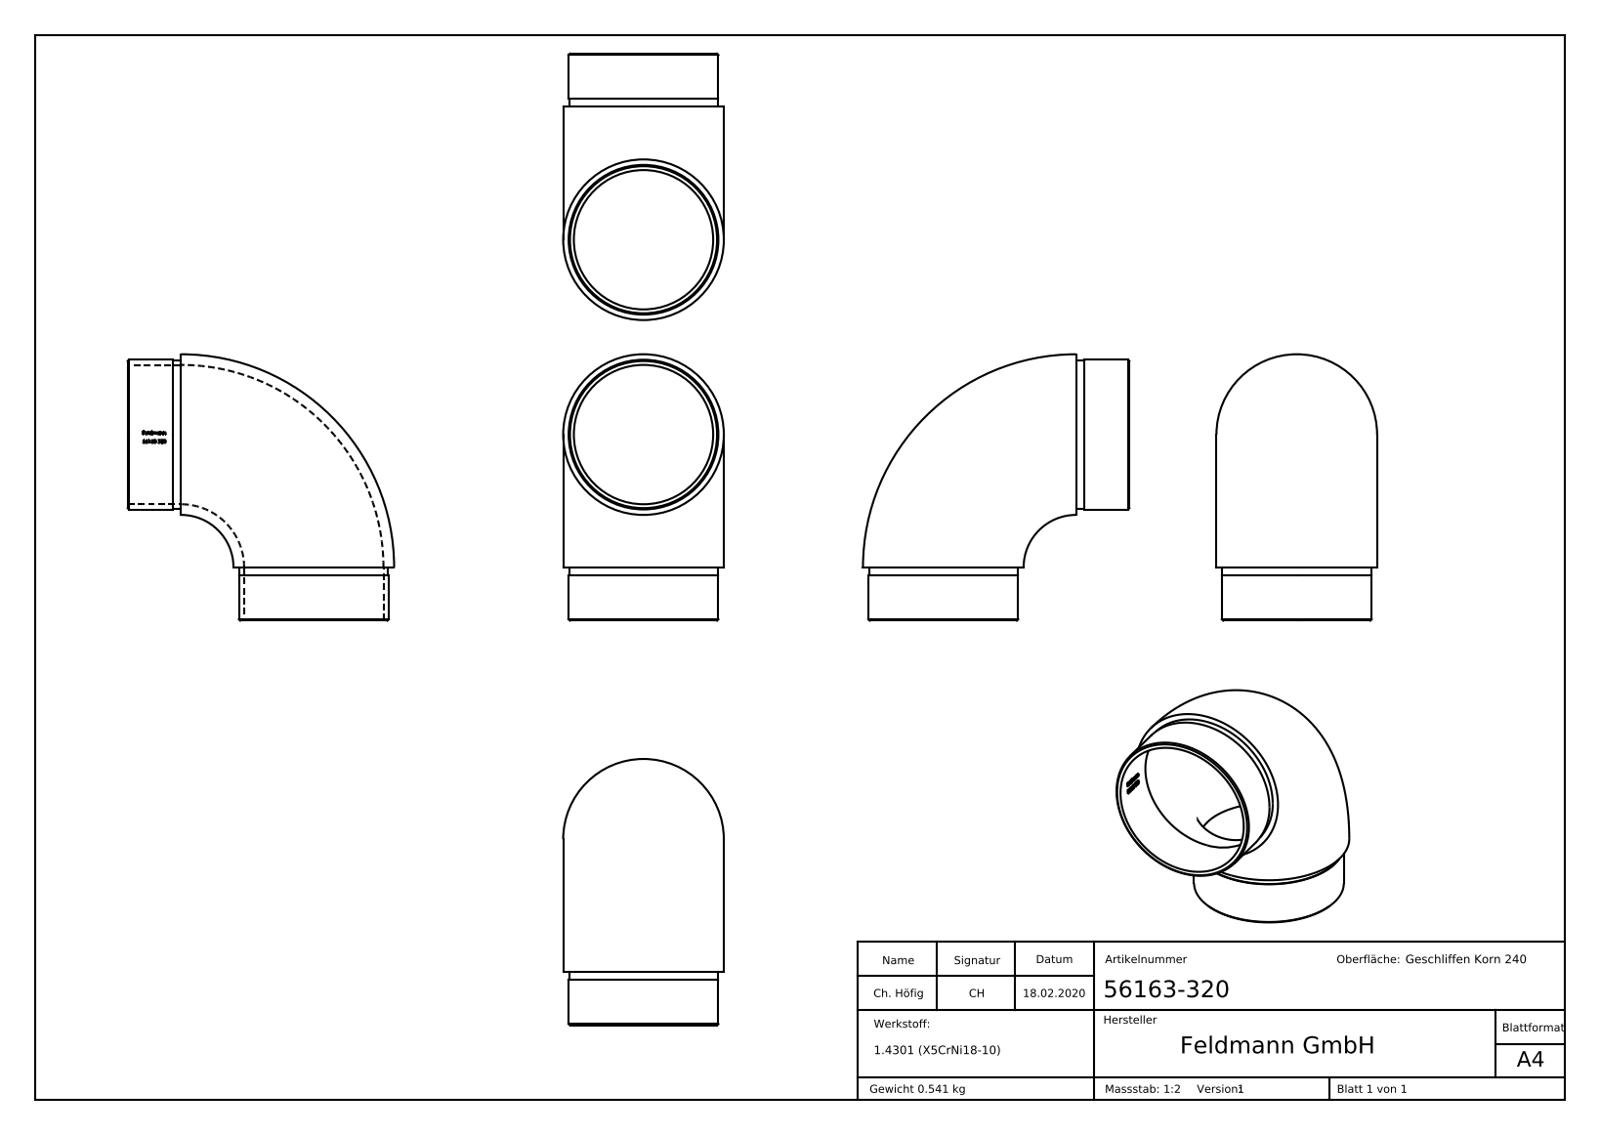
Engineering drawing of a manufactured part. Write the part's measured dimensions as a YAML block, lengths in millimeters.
part_name: "56163-320"
step_written_by: "SolidWorks 2015 (CONFIG_CONTROL_DESIGN)"
units: millimeters
bodies: {solids: 1, faces: 244, planar: 94, cylindrical: 29, other: 121}
overall_size: [100, 100, 60.3]
volume: 68437
surface_area: 42788
round_holes:
  - {diameter: 52.3, count: 2}
round_bosses_or_shafts:
  - {diameter: 56.2, count: 2}
  - {diameter: 55.8, count: 2}
partial_cylinders:
  - {radius: 26.25, count: 1}
face_to_face_distances: [20, 17, 3, 0.39, 1.26, 2.97, 1.32, 4.23, 3.66, 3.27]
